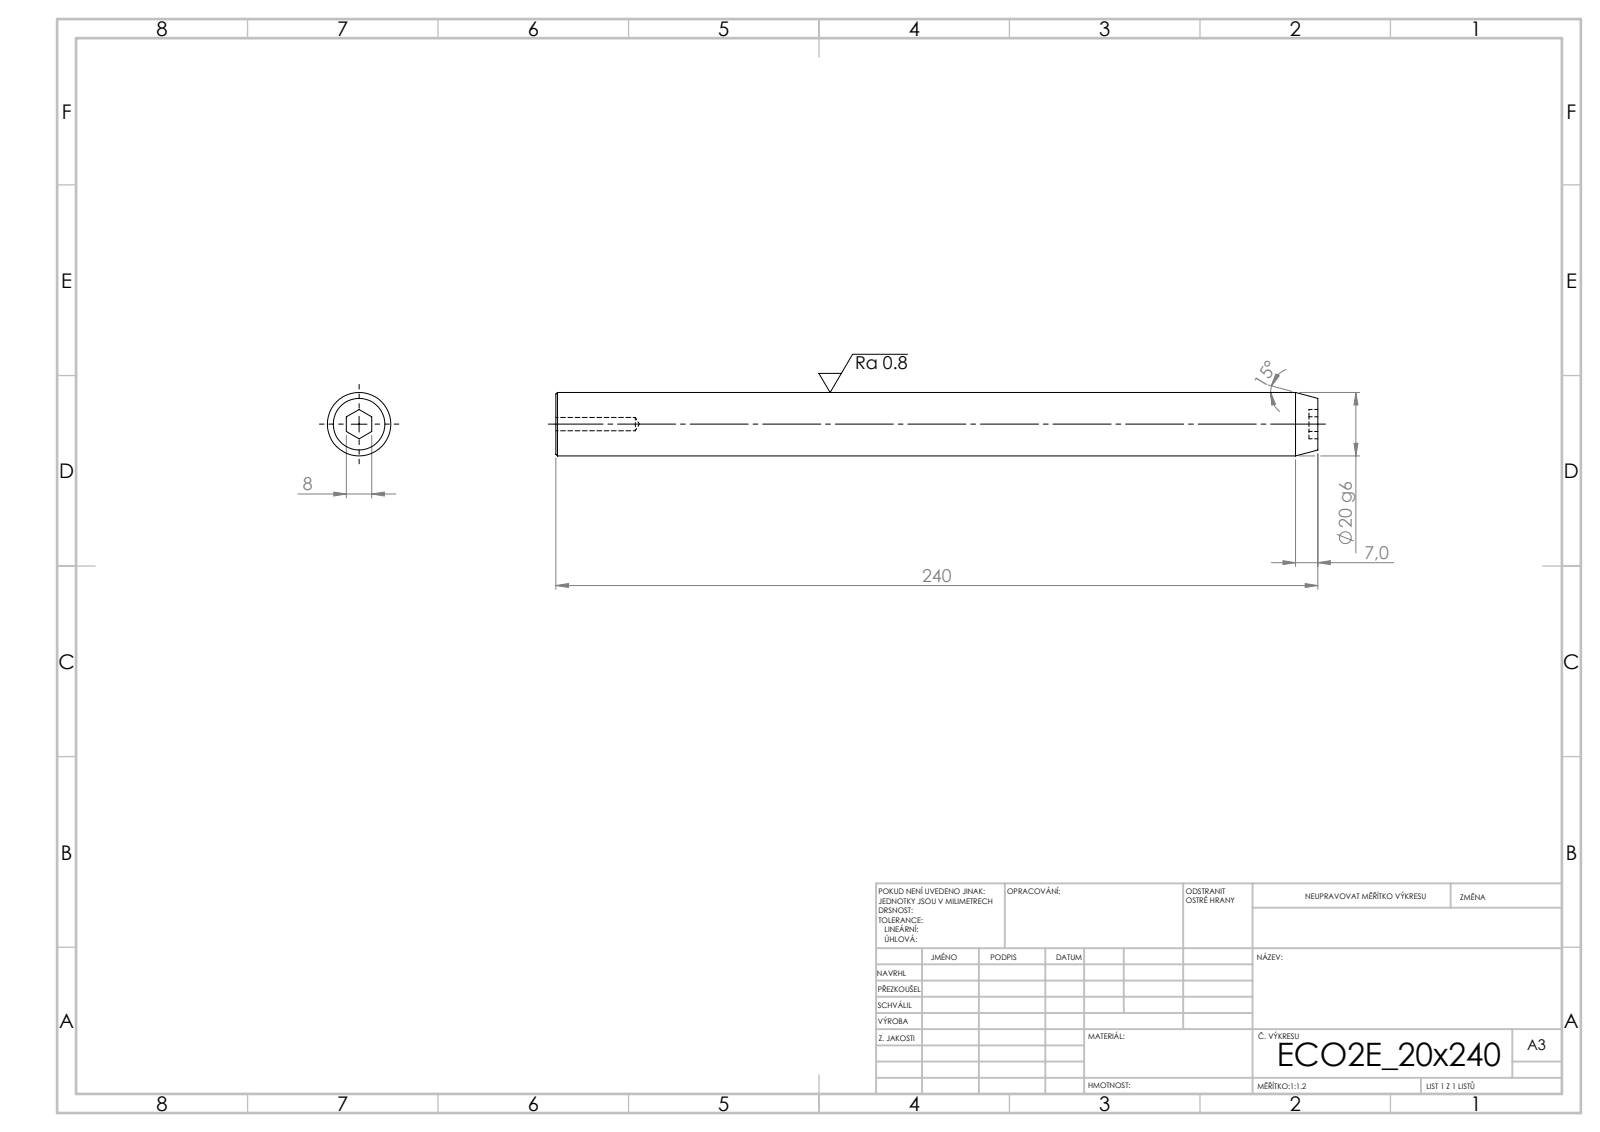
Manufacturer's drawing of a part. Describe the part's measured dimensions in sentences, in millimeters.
Its 3-D file was written by "SolidWorks 2019 (CONFIG_CONTROL_DESIGN)". It is 1 solid with 19 faces: 9 planar, 4 cylindrical and 6 other. Overall it measures 240 by 20 by 20 millimeters. Its volume is 74 496 cubic millimeters and its surface area 15 965 square millimeters. Round holes: 1 of diameter 4.2. Round bosses or shafts: 1 of diameter 20. The main face-to-face distances are 240, 2.8, 237.2, 8.
